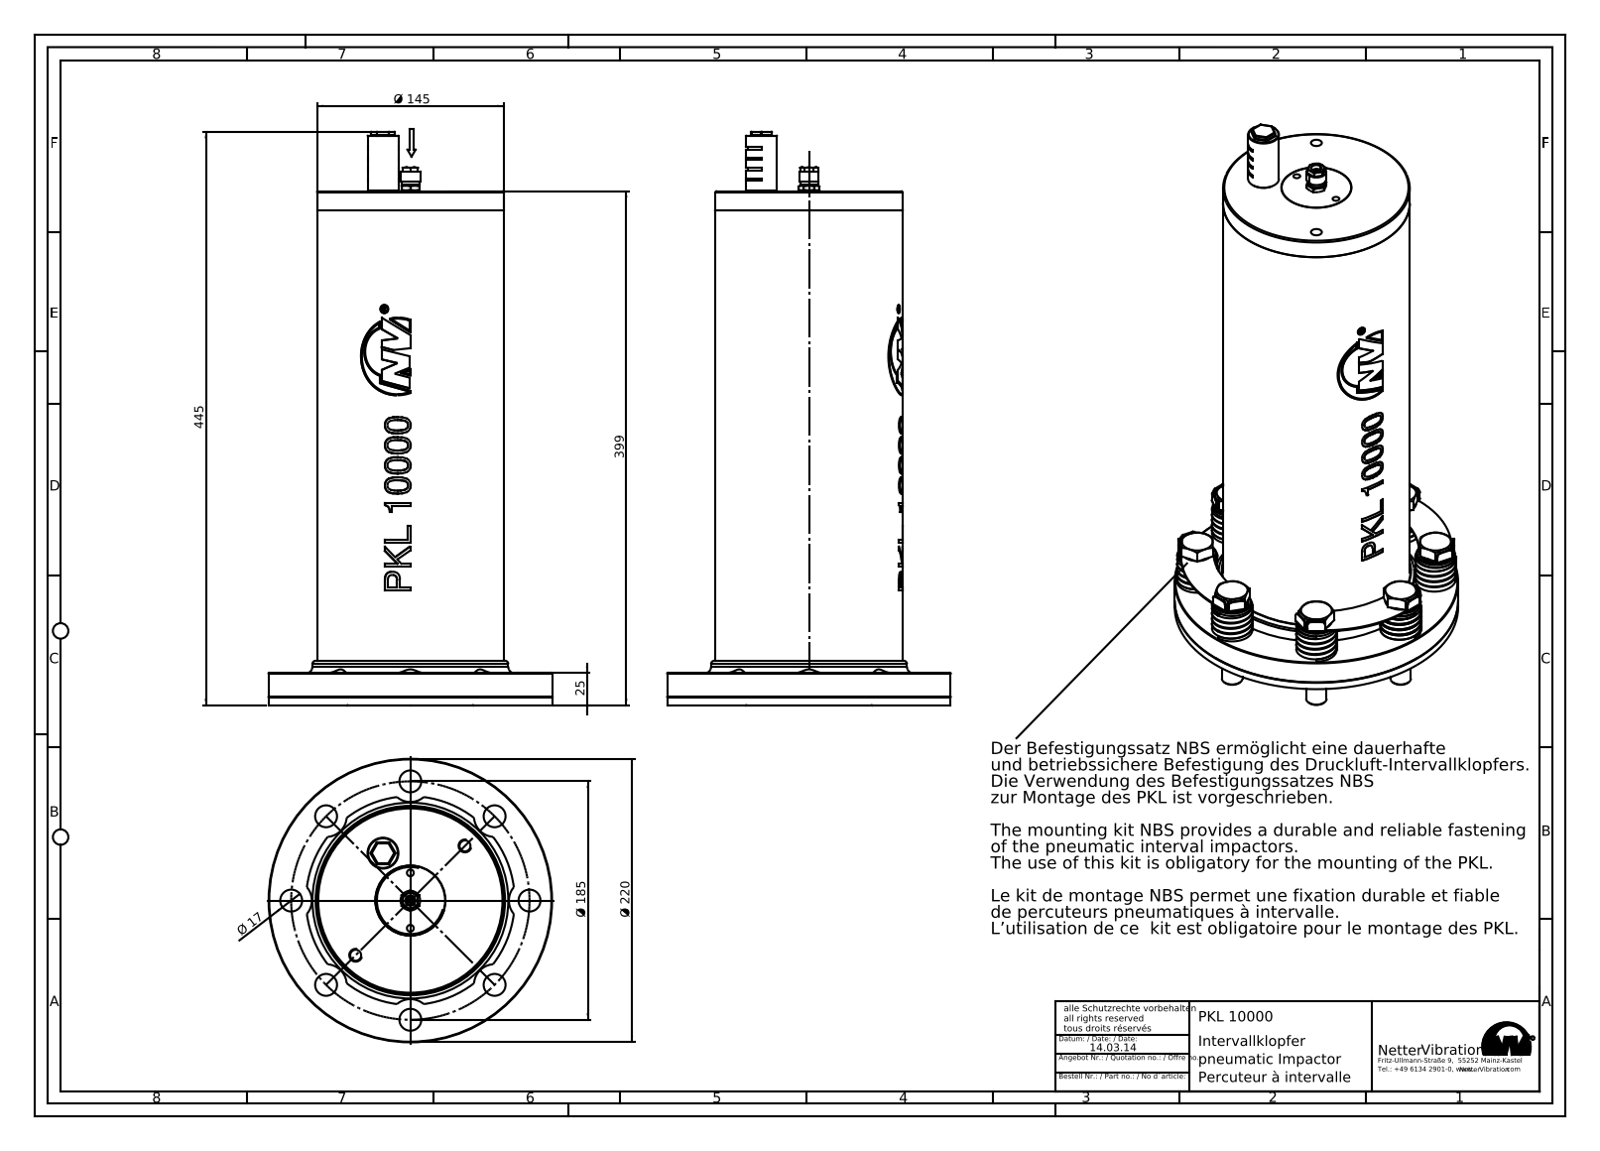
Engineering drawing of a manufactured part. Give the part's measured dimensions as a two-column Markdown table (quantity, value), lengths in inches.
| quantity | value |
| --- | --- |
| part name | PKL 10000 |
| STEP written by | SolidWorks 2010 (AUTOMOTIVE_DESIGN) |
| units | inches |
| bodies | 40 solids, 1419 faces (426 planar, 549 cylindrical, 444 other) |
| overall size | 18.406 × 8.661 × 8.661 |
| volume | 129.3 in³ |
| surface area | 1 142 in² |
| round holes (diameter × count) | 0.65 × 8, 0.669 × 8, 0.209 × 2, 0.335 × 2, 0.236 × 1, 0.268 × 1, 0.315 × 1, 0.337 × 1, 0.589 × 1, 1.909 × 1, 2.067 × 1, 2.15 × 1 |
| round bosses / shafts (diameter × count) | 0.945 × 9, 1.24 × 8, 1.181 × 8, 0.63 × 8, 8.661 × 1, 5.984 × 1, 5.709 × 1, 3.898 × 1 |
| partial cylindrical surfaces (radius × count) | 0.039 × 40, 0.098 × 28, 0.02 × 18, 0.079 × 16, 0.492 × 8, 0.63 × 8, 3.503 × 4, 0.433 × 1 |
| main face-to-face distances | 0.236, 0.984, 0.748, 15.709, 15.472, 14.724, 14.803, 14.567, 13.819, 0.906 |
| hole center spacings | 2.787, 3.642, 6.729, 2.584, 3.102, 3.739, 4.282, 4.341 |
